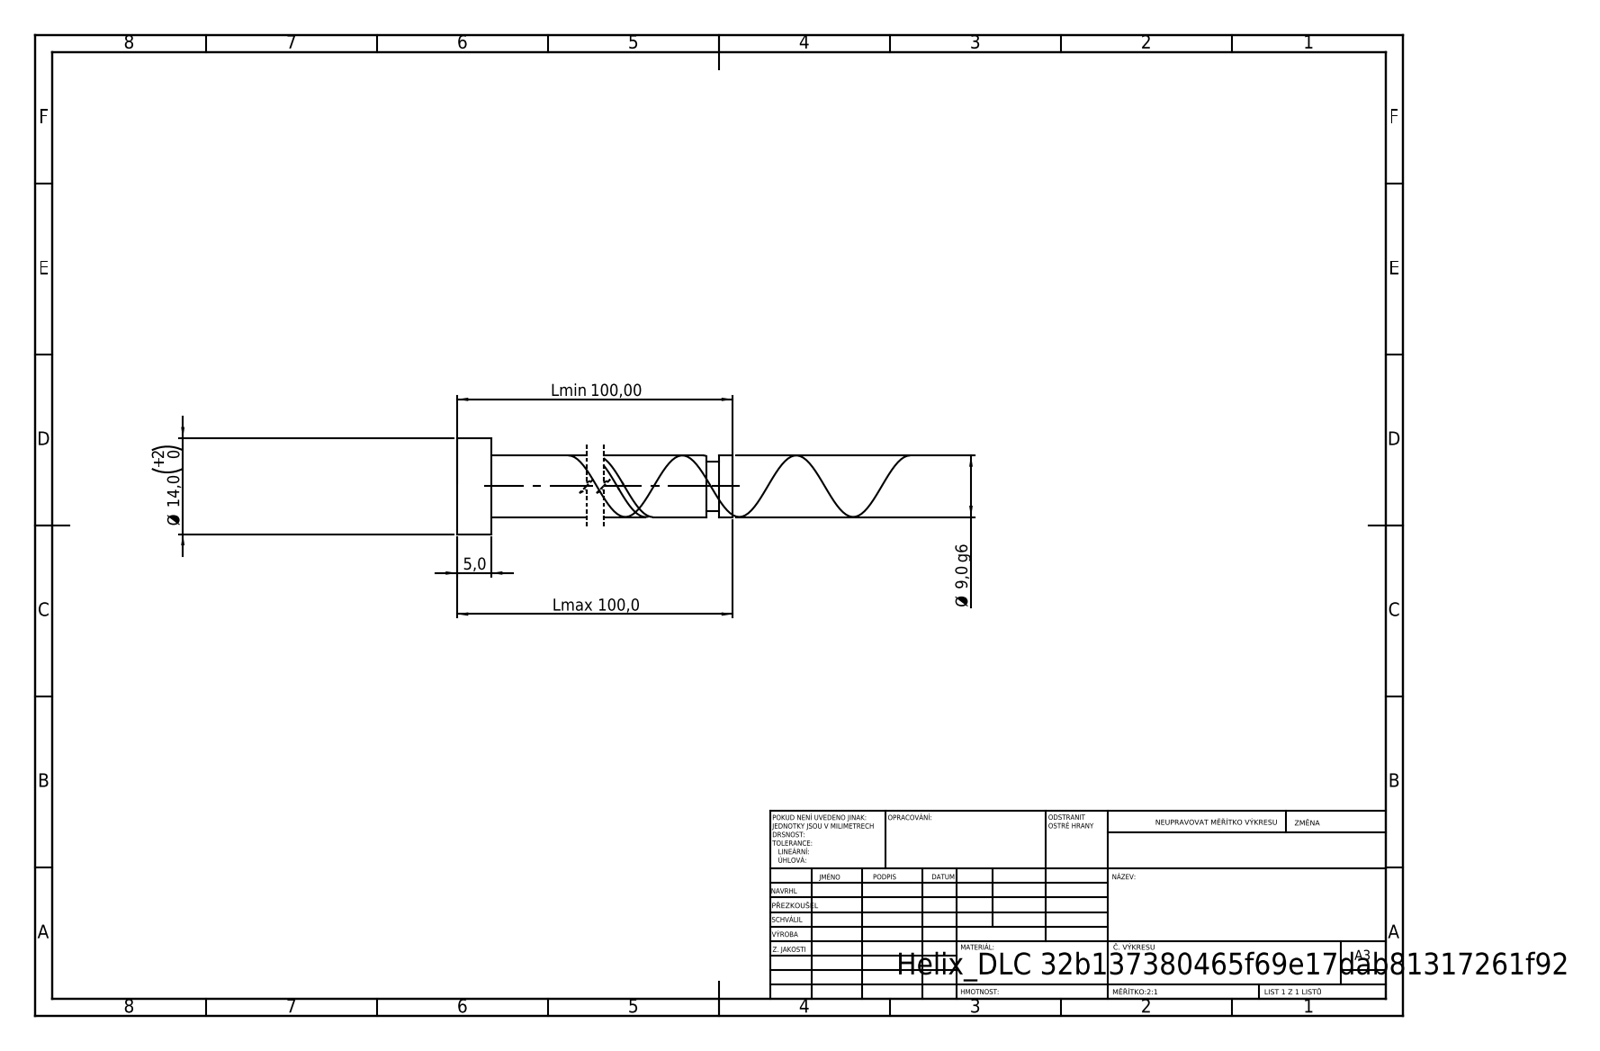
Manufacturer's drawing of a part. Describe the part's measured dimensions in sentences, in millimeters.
Its 3-D file was written by "SolidWorks 2019 (CONFIG_CONTROL_DESIGN)". It is 1 solid with 21 faces: 6 planar, 14 cylindrical and 1 other. Overall it measures 100 by 14 by 14 millimeters. Its volume is 6 711 cubic millimeters and its surface area 3 357 square millimeters. Round bosses or shafts: 1 of diameter 14, 1 of diameter 9, 1 of diameter 7.2. The main face-to-face distances are 5, 100, 95, 97.91, 92.91, 2.09, 96.11, 91.11, 1.8, 3.89.
